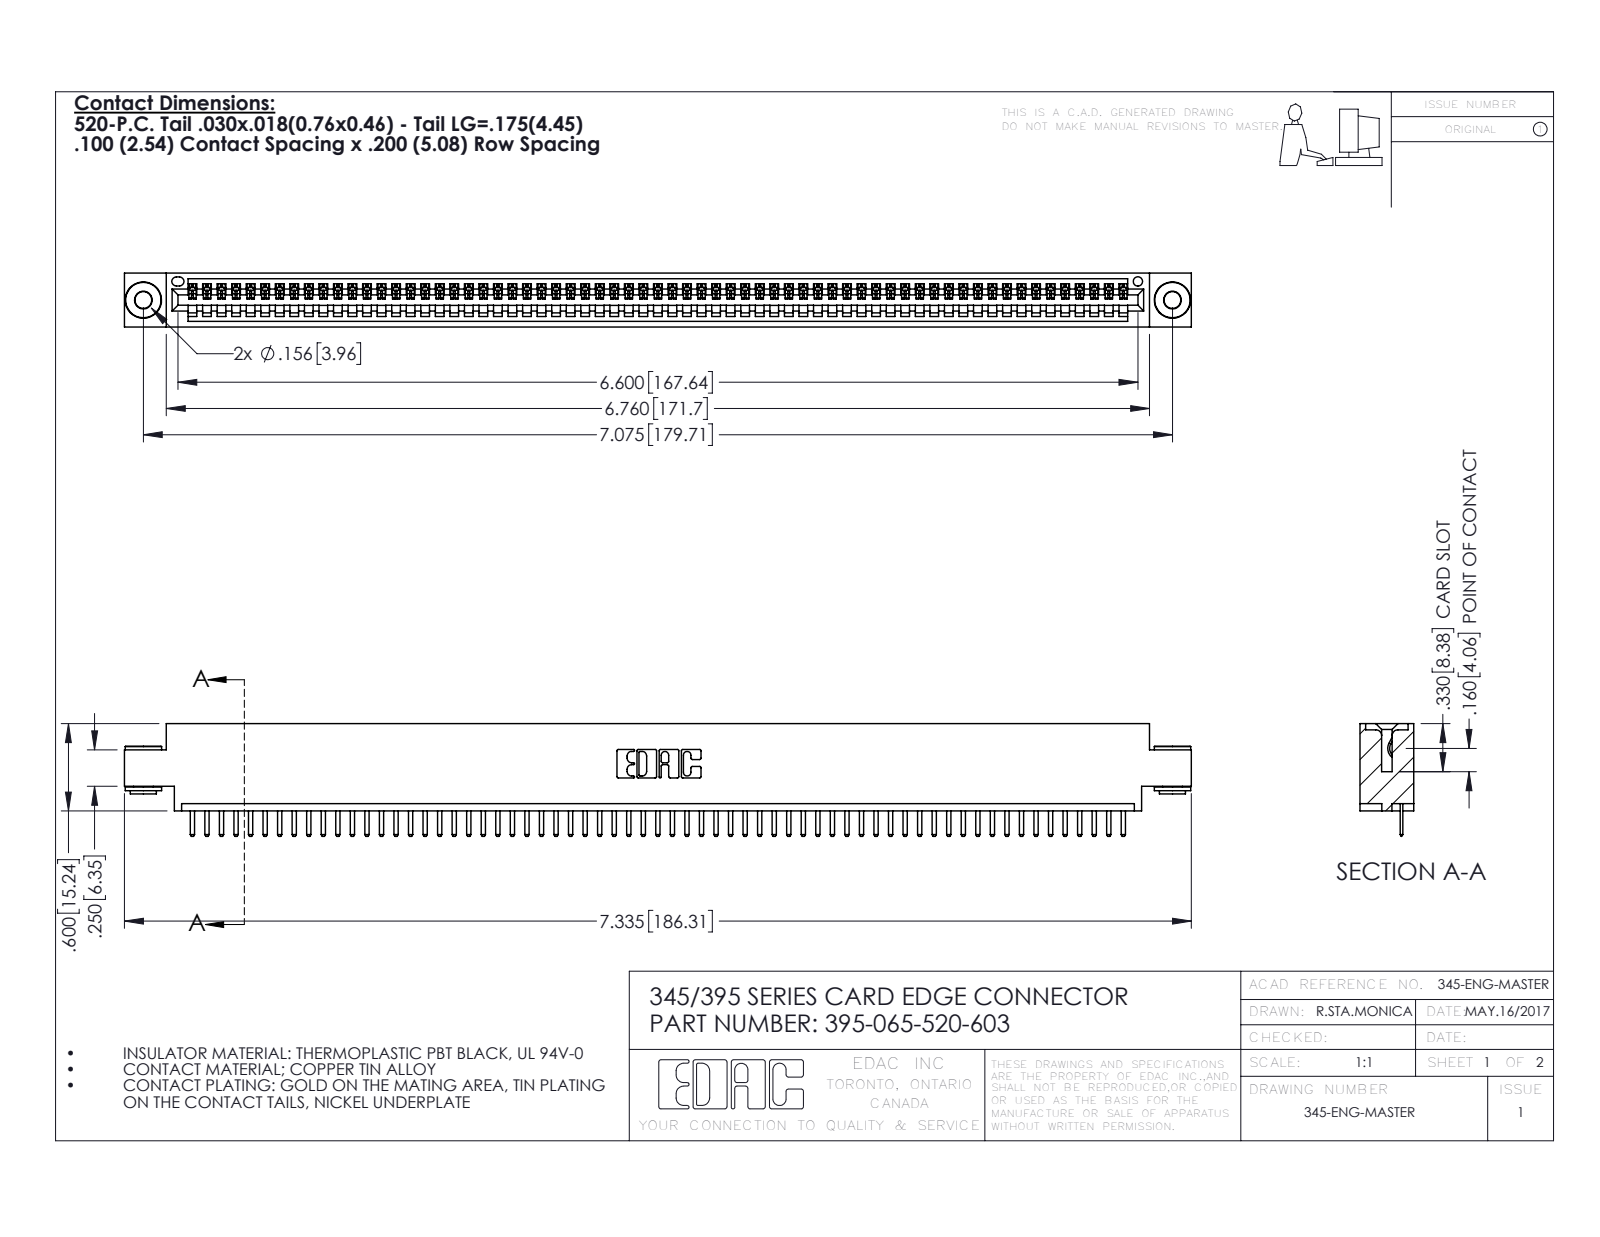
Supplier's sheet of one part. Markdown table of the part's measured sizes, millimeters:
| quantity | value |
| --- | --- |
| part name | 345-292-001_345-293-120; 345 Part_0.170 Offset - 0.156 Dia-TH; 395-065-520-603; 345-250-002_345-250-002-102 |
| STEP written by | SolidWorks 2016 (CONFIG_CONTROL_DESIGN) |
| units | millimeters |
| bodies | 68 solids, 4198 faces (2824 planar, 1366 cylindrical, 8 other) |
| overall size | 186.3 × 19.7 × 9.4 |
| volume | 17 600 mm³ |
| surface area | 23 430 mm² |
| round holes (diameter × count) | 2.9 × 2, 4 × 2, 1.6 × 1 |
| round bosses / shafts (diameter × count) | 6.4 × 2, 4.6 × 2, 3.5 × 2 |
| partial cylindrical surfaces (radius × count) | 0.3 × 132, 0.2 × 130, 0.3 × 22, 0.2 × 6, 0.8 × 6, 0.7 × 3, 0.8 × 2, 1 × 2 |
| main face-to-face distances | 1.8, 7.6, 9.4, 5.1, 2.5, 6.9, 0.6, 5.7, 1.8, 4.4 |
| hole center spacings | 6.9, 173.7, 179.7 |
